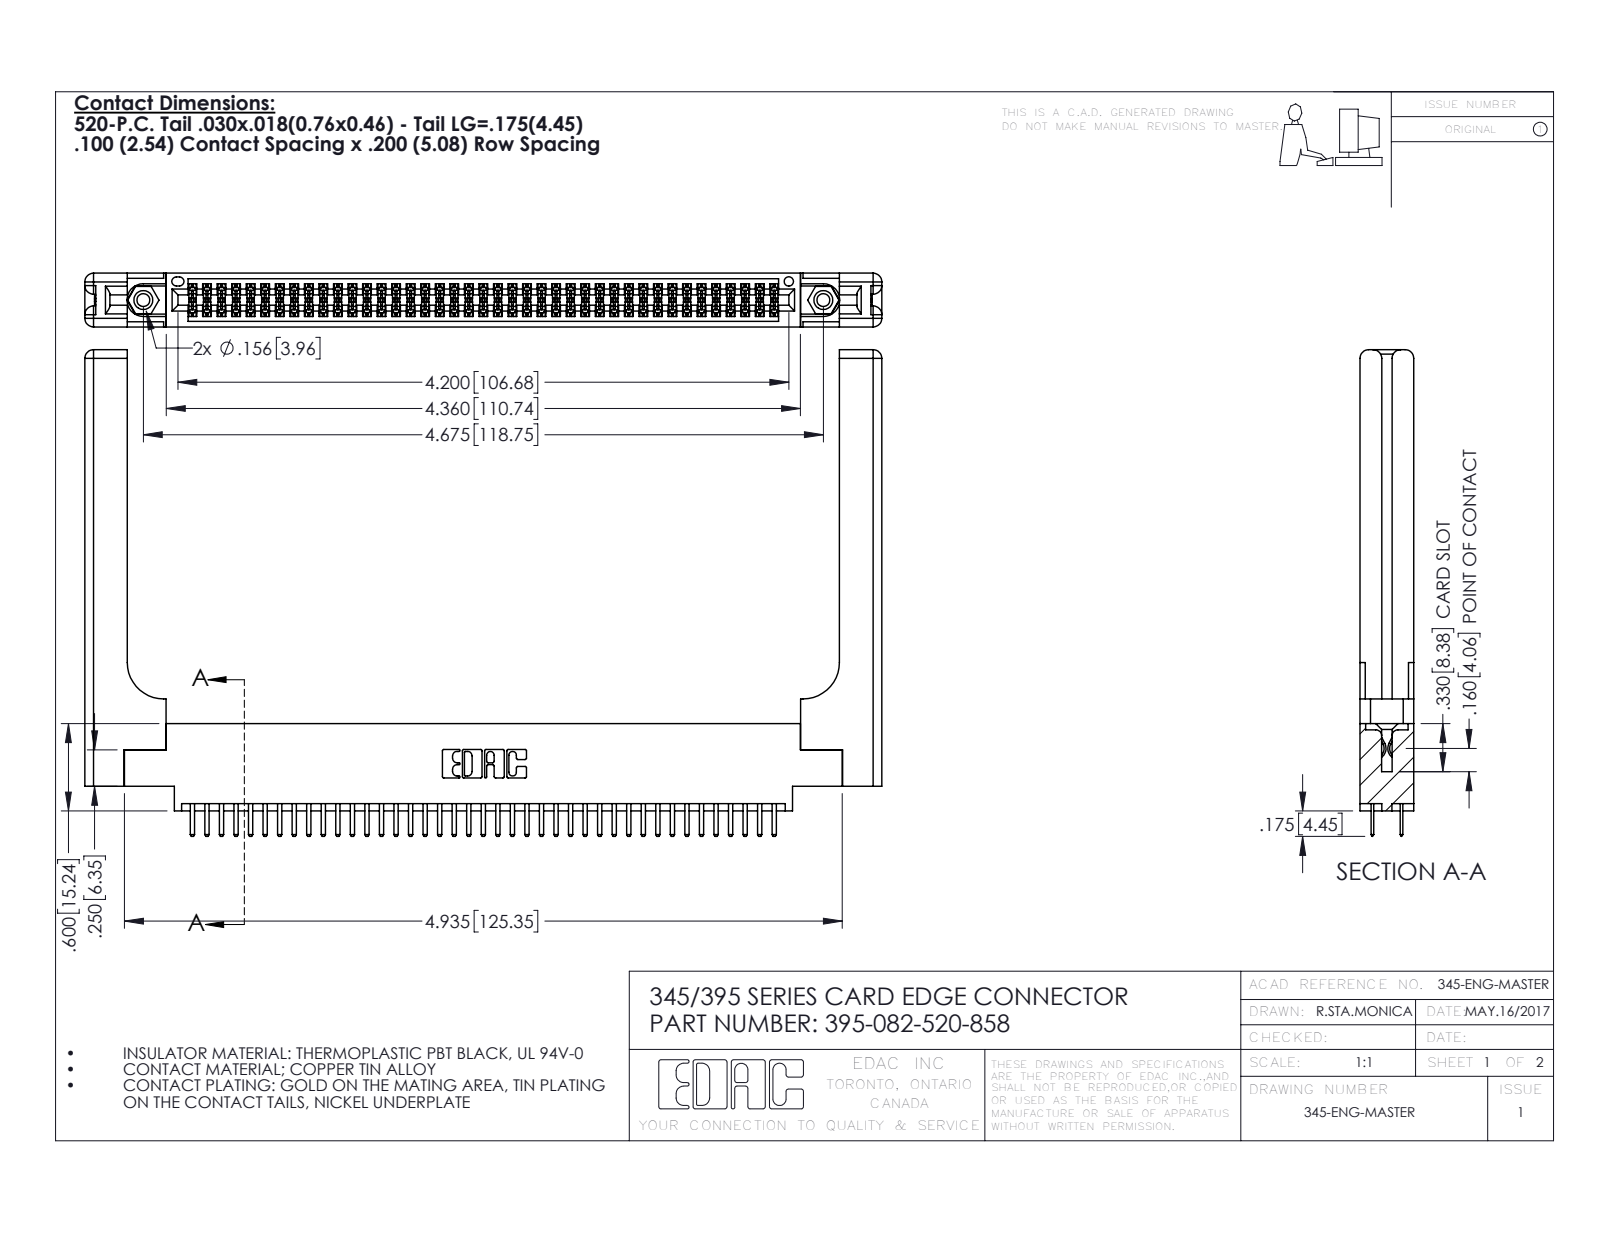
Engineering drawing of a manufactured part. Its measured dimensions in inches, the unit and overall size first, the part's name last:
Units: inches
Overall size (bounding box): 5.479 × 3.345 × 0.37
Round holes (diameter × count): ⌀0.089 ×2, ⌀0.125 ×2, ⌀0.156 ×2, ⌀0.064 ×1
Round bosses / shafts (diameter × count): ⌀0.155 ×2
Partial cylindrical surfaces — rounded edges, fillets, slot ends (radius × count): R0.006 ×123, R0.01 ×86, R0.01 ×22, R0.06 ×16, R0.007 ×6, R0.031 ×6, R0.026 ×3, R0.014 ×2
Main face-to-face distances: 0.37, 0.072, 0.298, 0.2, 0.098, 0.272, 0.025, 0.225, 0.148, 0.15
Hole centre spacings: 0.27, 4.439, 4.675
Volume: 1.332 in³ · Surface area: 38.52 in²
Bodies: 87 solids, 4814 faces (3102 planar, 1652 cylindrical, 60 other)
Part name (STEP PRODUCT): 345-250-001_345-250-001-102; 345 Part_0.170 Offset - 0.156 Dia-TH; 395-082-520-858; 345-292-001_345-293-120 (+1 more)
STEP written by: SolidWorks 2016 (CONFIG_CONTROL_DESIGN)
